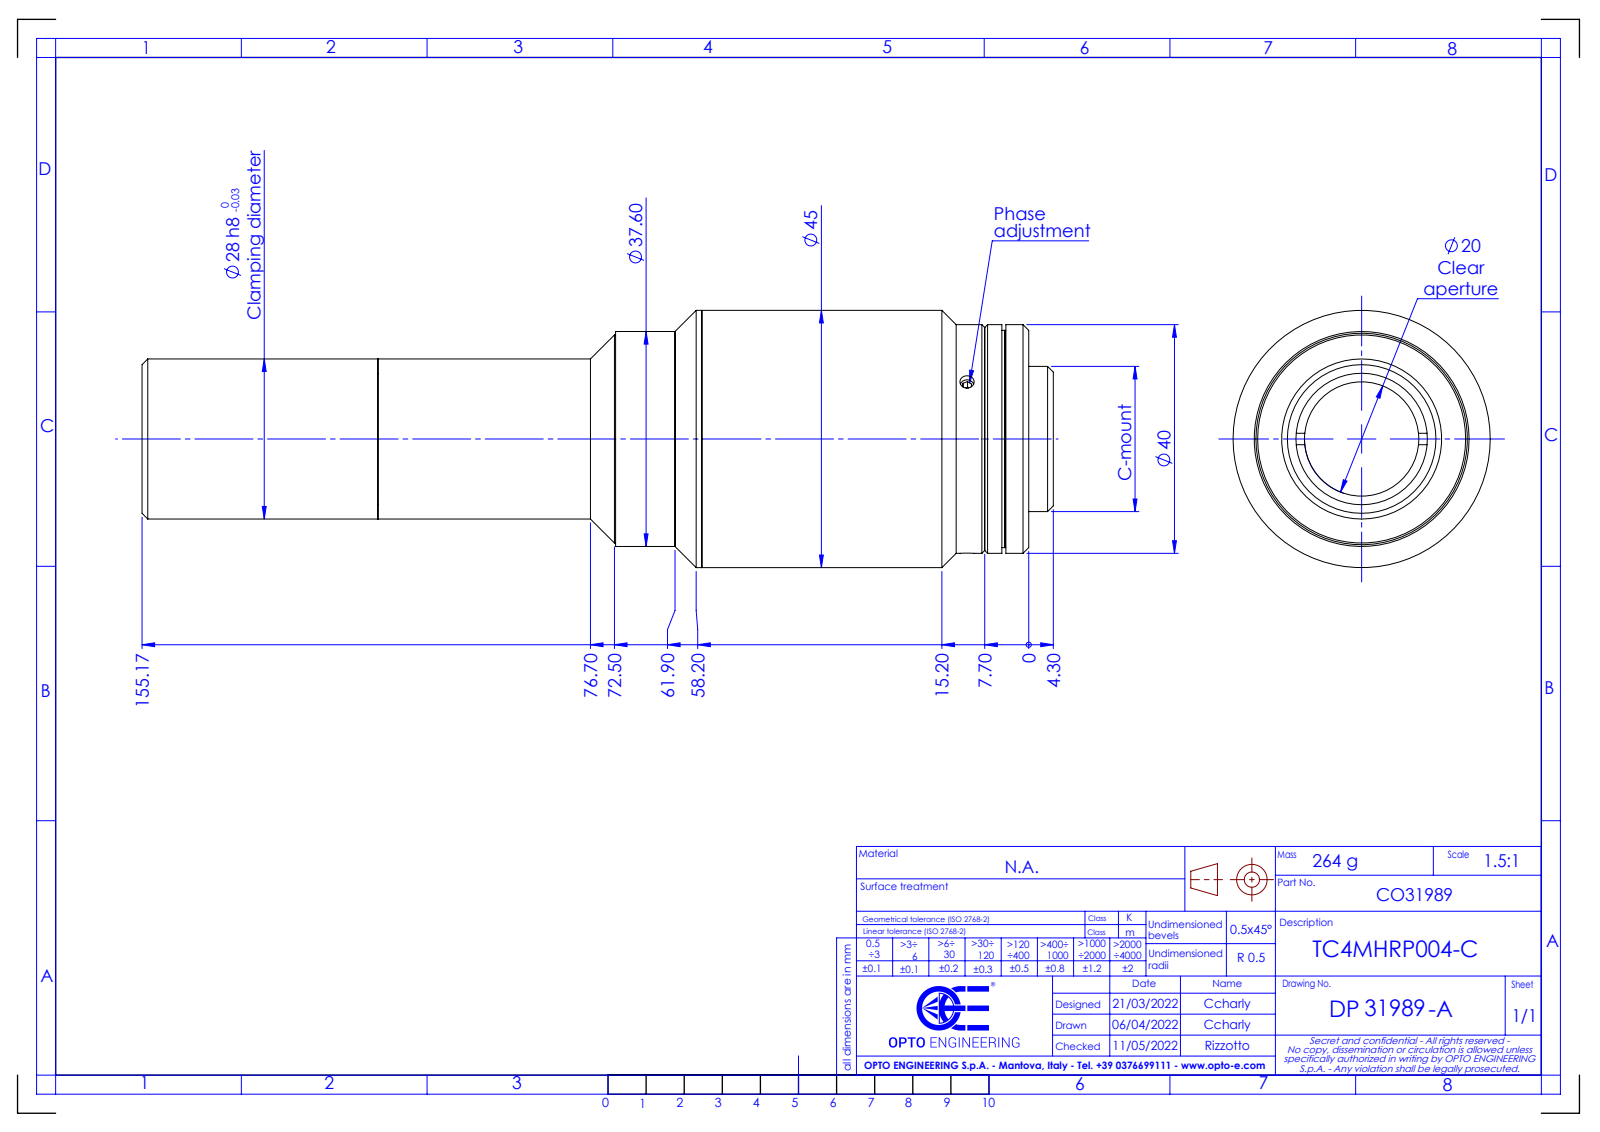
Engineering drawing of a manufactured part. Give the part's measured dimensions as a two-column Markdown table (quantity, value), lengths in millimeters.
| quantity | value |
| --- | --- |
| part name | DP31989-A_TC4MHRP004-C |
| STEP written by | SolidWorks 2021 (CONFIG_CONTROL_DESIGN) |
| units | millimeters |
| bodies | 0 solids, 89 faces (33 planar, 32 cylindrical, 24 other) |
| overall size | 159.47 × 45 × 45 |
| round holes (diameter × count) | 2.5 × 3, 20 × 1, 22.5 × 1, 23 × 1 |
| round bosses / shafts (diameter × count) | 45 × 1, 40 × 1, 37.6 × 1, 36.4 × 1, 28 × 1, 25.4 × 1 |
| main face-to-face distances | 3.7, 3, 0.7, 4.7, 7.7, 4, 106.19, 109.19, 109.89, 113.89 |
